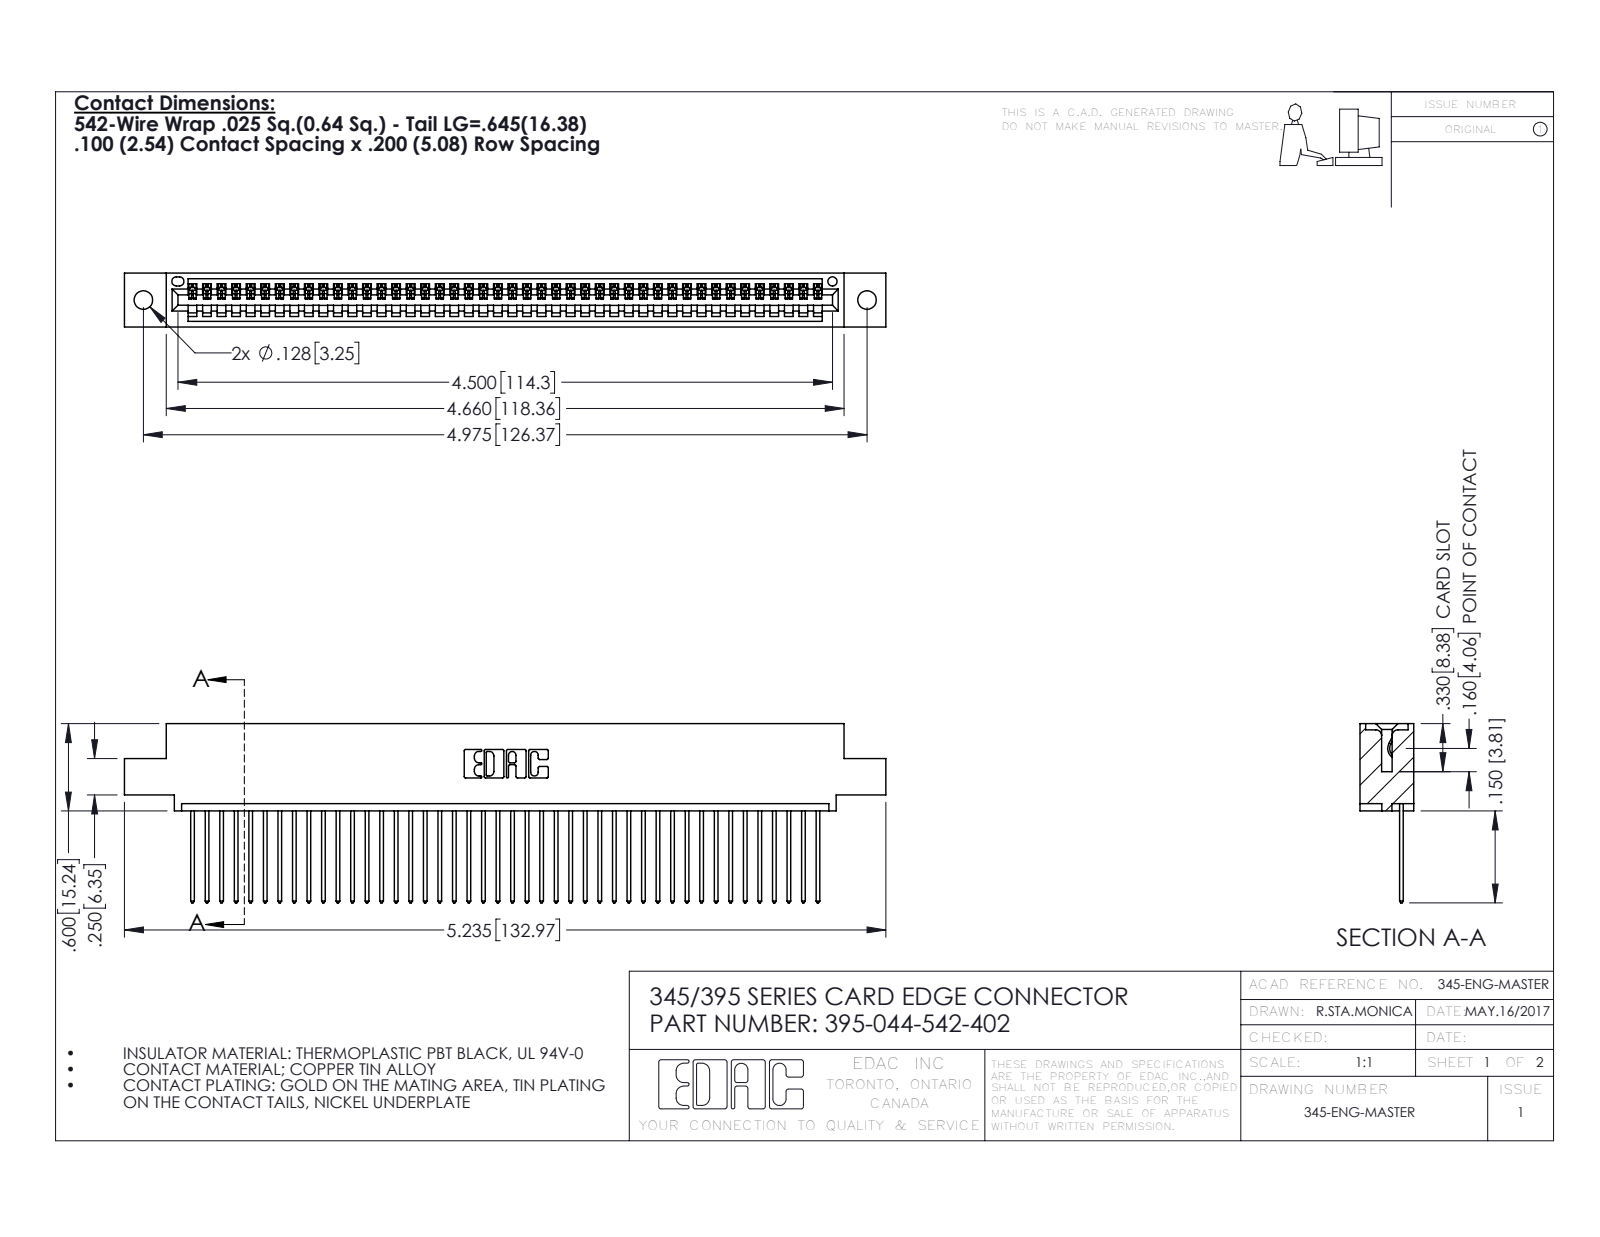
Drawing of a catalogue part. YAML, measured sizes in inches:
part_name: "395-044-542-402; 345 Part_0.110 Offset - 0.128 Dia; 345-292-001_345-293-142"
step_written_by: "SolidWorks 2016 (CONFIG_CONTROL_DESIGN)"
units: inches
bodies: {solids: 45, faces: 2682, planar: 1844, cylindrical: 838, other: 0}
overall_size: [5.235, 1.232, 0.37]
volume: 0.771
surface_area: 26.73
round_holes:
  - {diameter: 0.128, count: 2}
  - {diameter: 0.064, count: 1}
partial_cylinders:
  - {radius: 0.006, count: 88}
  - {radius: 0.01, count: 88}
  - {radius: 0.01, count: 22}
  - {radius: 0.007, count: 6}
  - {radius: 0.031, count: 6}
  - {radius: 0.026, count: 3}
  - {radius: 0.031, count: 2}
  - {radius: 0.04, count: 2}
face_to_face_distances: [0.072, 0.298, 0.37, 0.098, 0.272, 0.025, 0.2, 0.225, 0.149, 0.072]
hole_center_spacings: [0.27, 4.739, 4.975]
